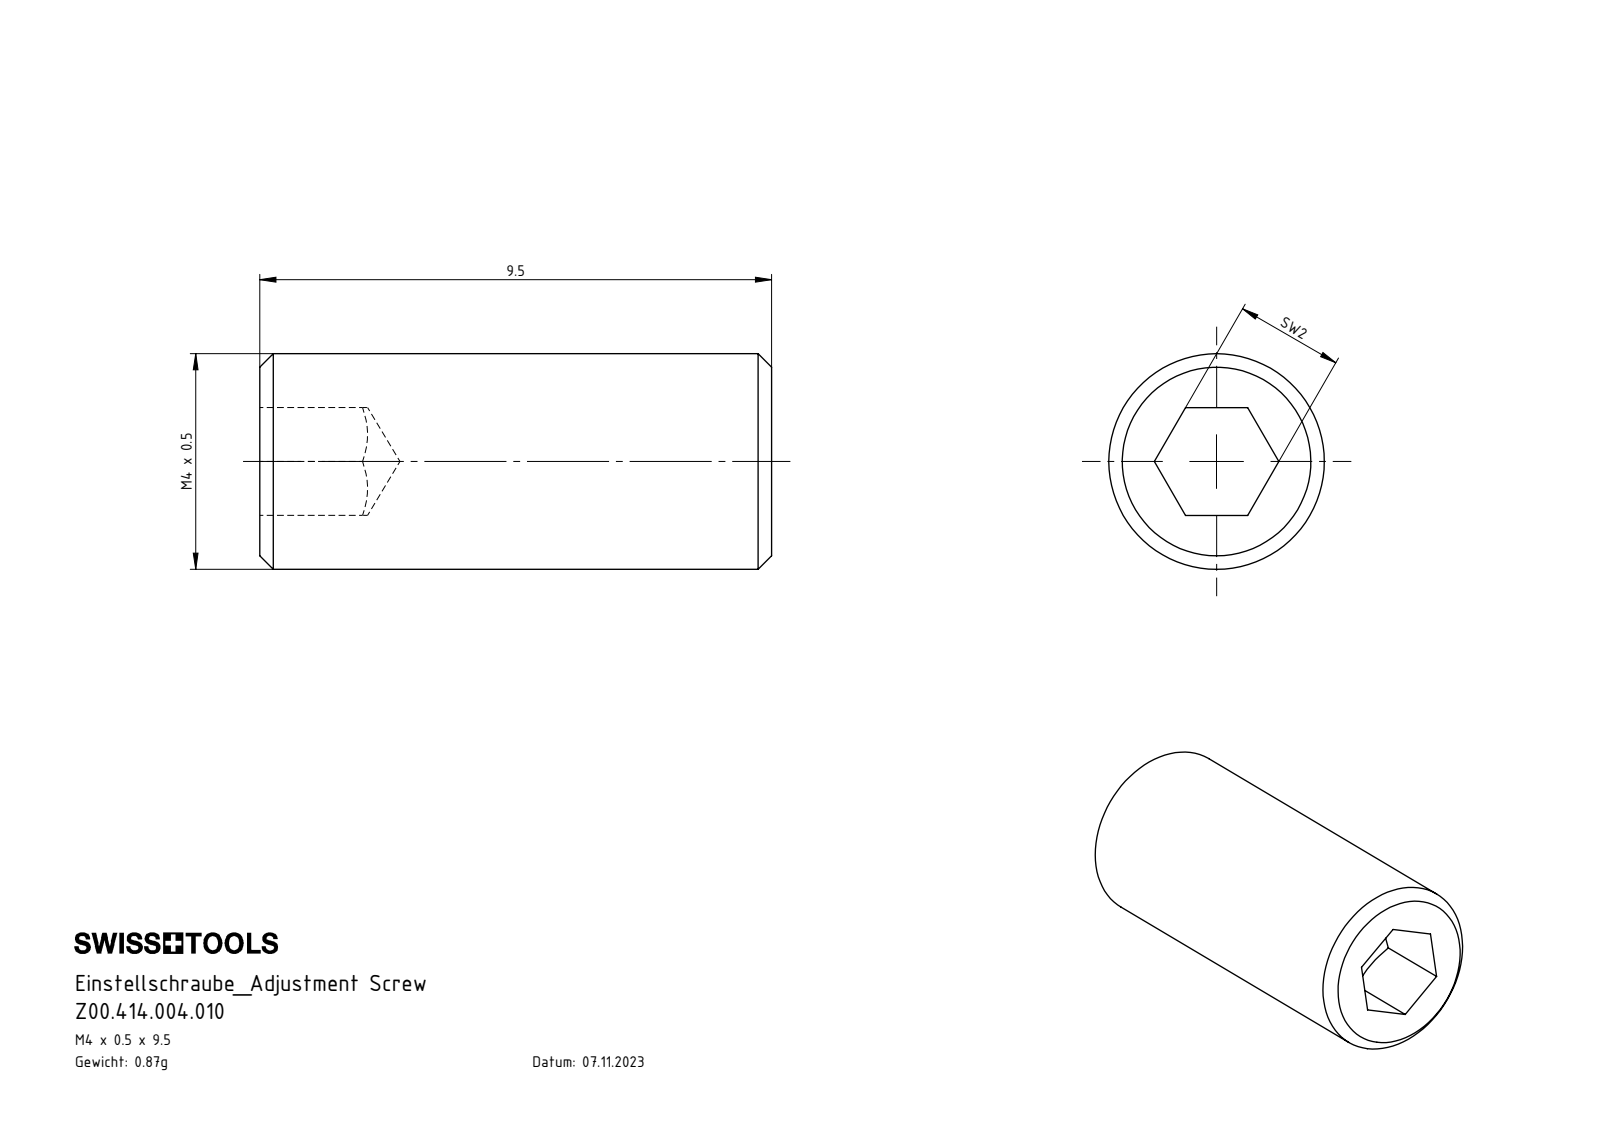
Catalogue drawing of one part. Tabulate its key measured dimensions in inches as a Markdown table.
| quantity | value |
| --- | --- |
| part name | Z00.414.004.010 |
| STEP written by | SolidWorks 2022 (AUTOMOTIVE_DESIGN) |
| units | inches |
| bodies | 1 solid, 16 faces (8 planar, 2 cylindrical, 6 other) |
| overall size | 0.374 × 0.157 × 0.157 |
| volume | 0.007 in³ |
| surface area | 0.24 in² |
| round bosses / shafts (diameter × count) | 0.157 × 1 |
| main face-to-face distances | 0.079, 0.374 |
